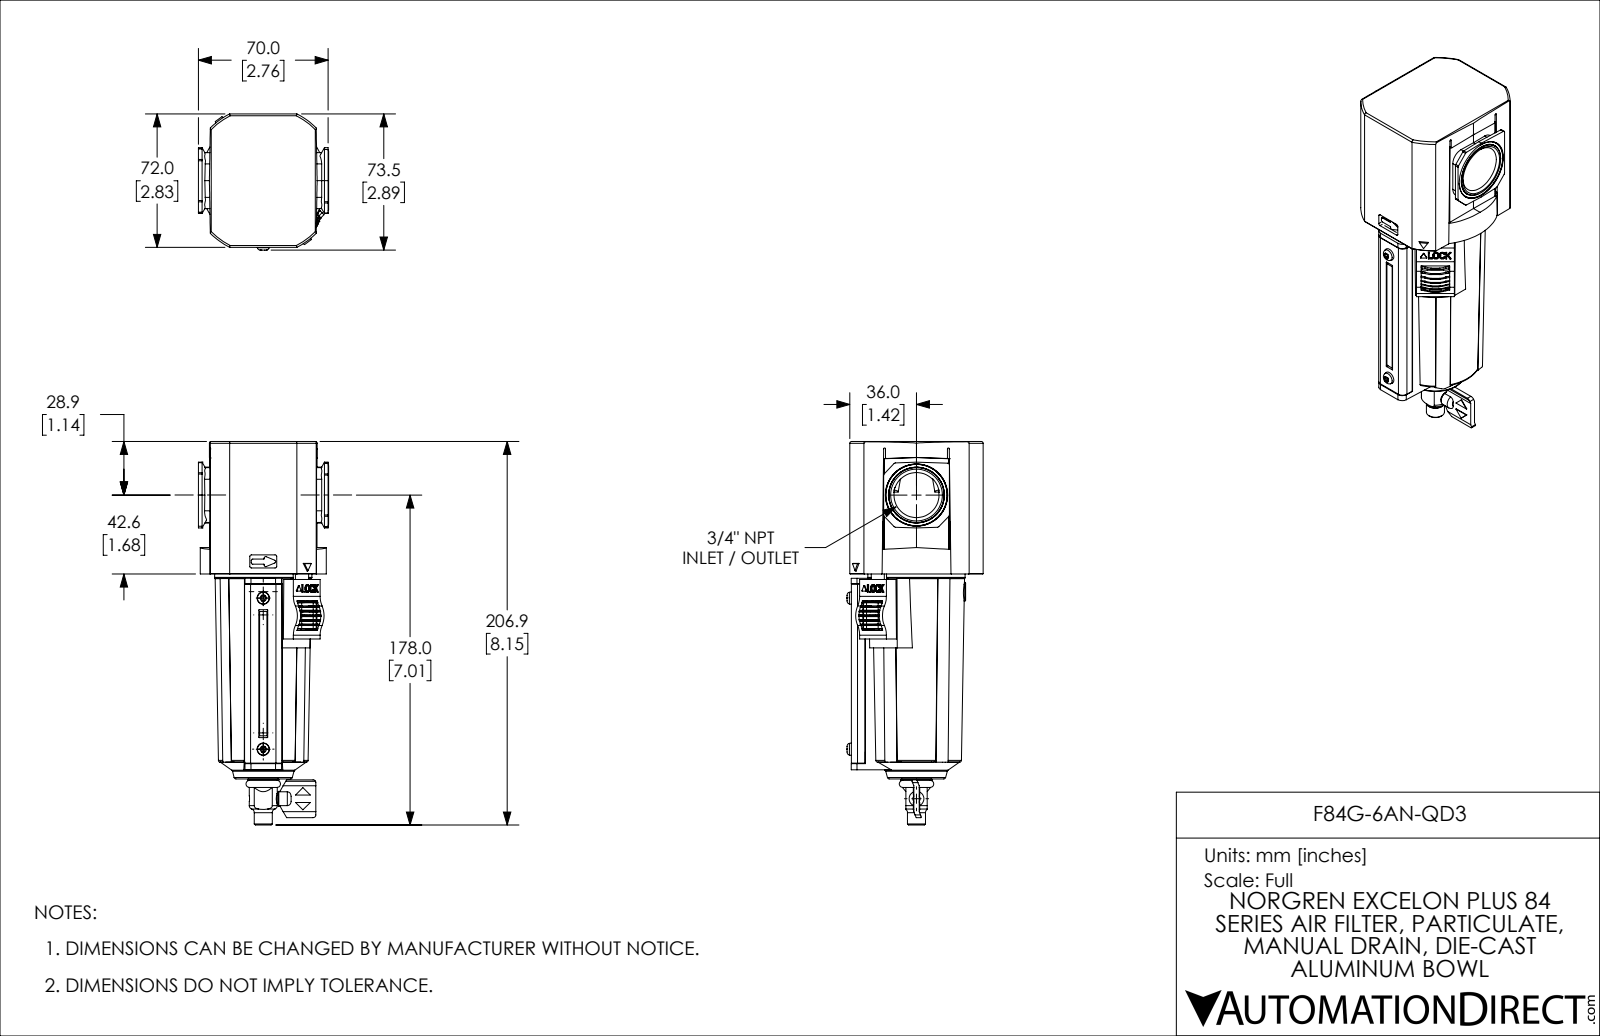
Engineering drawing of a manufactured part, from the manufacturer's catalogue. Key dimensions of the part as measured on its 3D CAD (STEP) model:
Part name (STEP PRODUCT): F84G-6AN-QD3
STEP written by: SolidWorks 2021 (CONFIG_CONTROL_DESIGN)
Units: inches
Bodies: 6 solids, 1221 faces (529 planar, 430 cylindrical, 262 other)
Overall size (bounding box): 8.146 × 2.892 × 2.766
Volume: 28 in³ · Surface area: 168.6 in²
Round holes (diameter × count): ⌀0.112 ×2, ⌀0.163 ×2, ⌀0.123 ×1, ⌀0.126 ×1, ⌀0.236 ×1, ⌀0.25 ×1, ⌀0.374 ×1, ⌀0.633 ×1, ⌀2.461 ×1
Round bosses / shafts (diameter × count): ⌀0.315 ×3, ⌀0.276 ×2, ⌀0.213 ×2, ⌀2.122 ×1, ⌀2.067 ×1, ⌀2.018 ×1, ⌀1.959 ×1, ⌀1.953 ×1
Partial cylindrical surfaces — rounded edges, fillets, slot ends (radius × count): R0.039 ×47, R0.02 ×37, R0.028 ×28, R0.01 ×18, R0.008 ×8, R0.038 ×8, R0.045 ×8, R0.06 ×8
Main face-to-face distances: 0.059, 2.352, 2.411, 2.047, 0.378, 2.457, 2.835, 0.364, 1.988, 2.756
Hole centre spacings: 0.594, 1.189, 2.504
